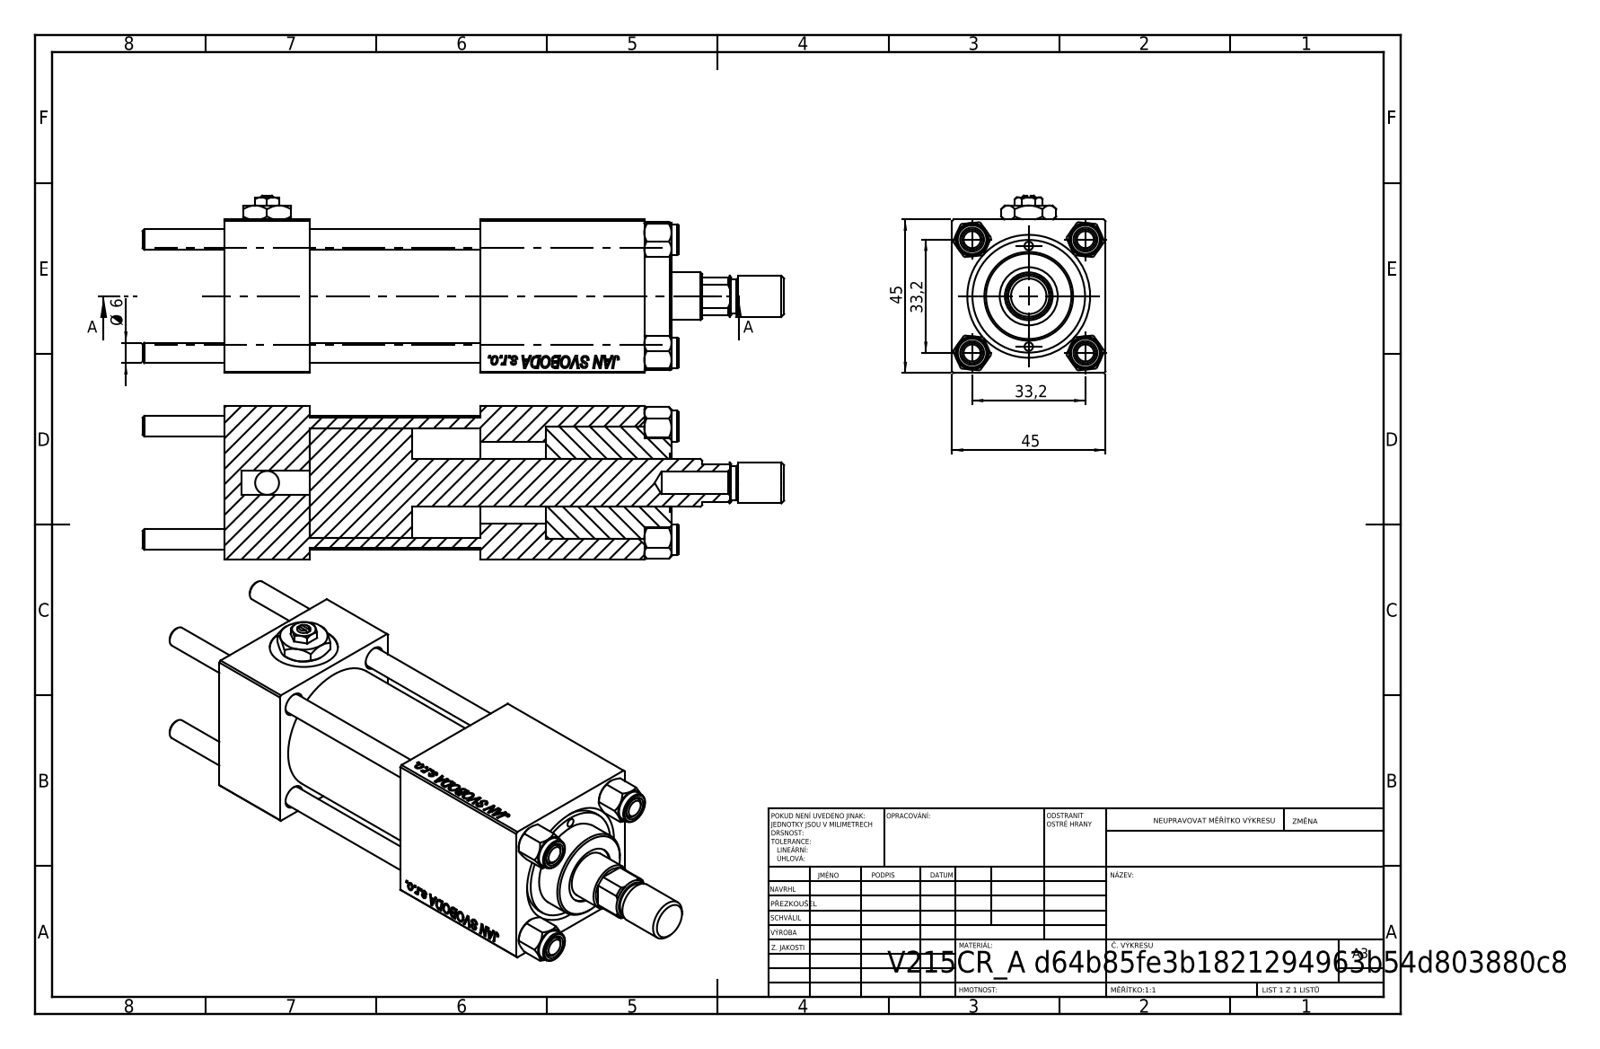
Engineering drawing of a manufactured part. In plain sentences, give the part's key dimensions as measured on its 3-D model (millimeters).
The part is named "CR025_012_A_0_G_A_G_M_020_+#_##_TYCINKA; Zatka_pro_OIL_PORT; ROD_END_AH; V215_VC_A (+3 more)". Its 3-D file was written by "SolidWorks 2019 (CONFIG_CONTROL_DESIGN)". It is 13 solids with 1204 faces: 548 planar, 92 cylindrical and 564 other. Overall it measures 188 by 52 by 45 millimeters. Its volume is 199 139 cubic millimeters and its surface area 74 831 square millimeters. Round holes: 4 of diameter 6, 2 of diameter 2.5, 2 of diameter 7, 2 of diameter 13.16, 2 of diameter 20, 1 of diameter 6.5, 1 of diameter 14, 1 of diameter 17, 1 of diameter 24, 1 of diameter 32, 1 of diameter 33. Round bosses or shafts: 4 of diameter 9, 1 of diameter 38, 1 of diameter 26, 1 of diameter 12, 1 of diameter 10. Partial cylindrical surfaces (rounded edges, fillets, slot ends): 1 of radius 6.5. The main face-to-face distances are 45, 25, 123, 98, 50, 75, 48, 94.3, 69.3, 19.3. The hole center spacings are 16.7, 23.48, 33.2, 35.47, 14.75, 46.95, 29.5, 75.5.
